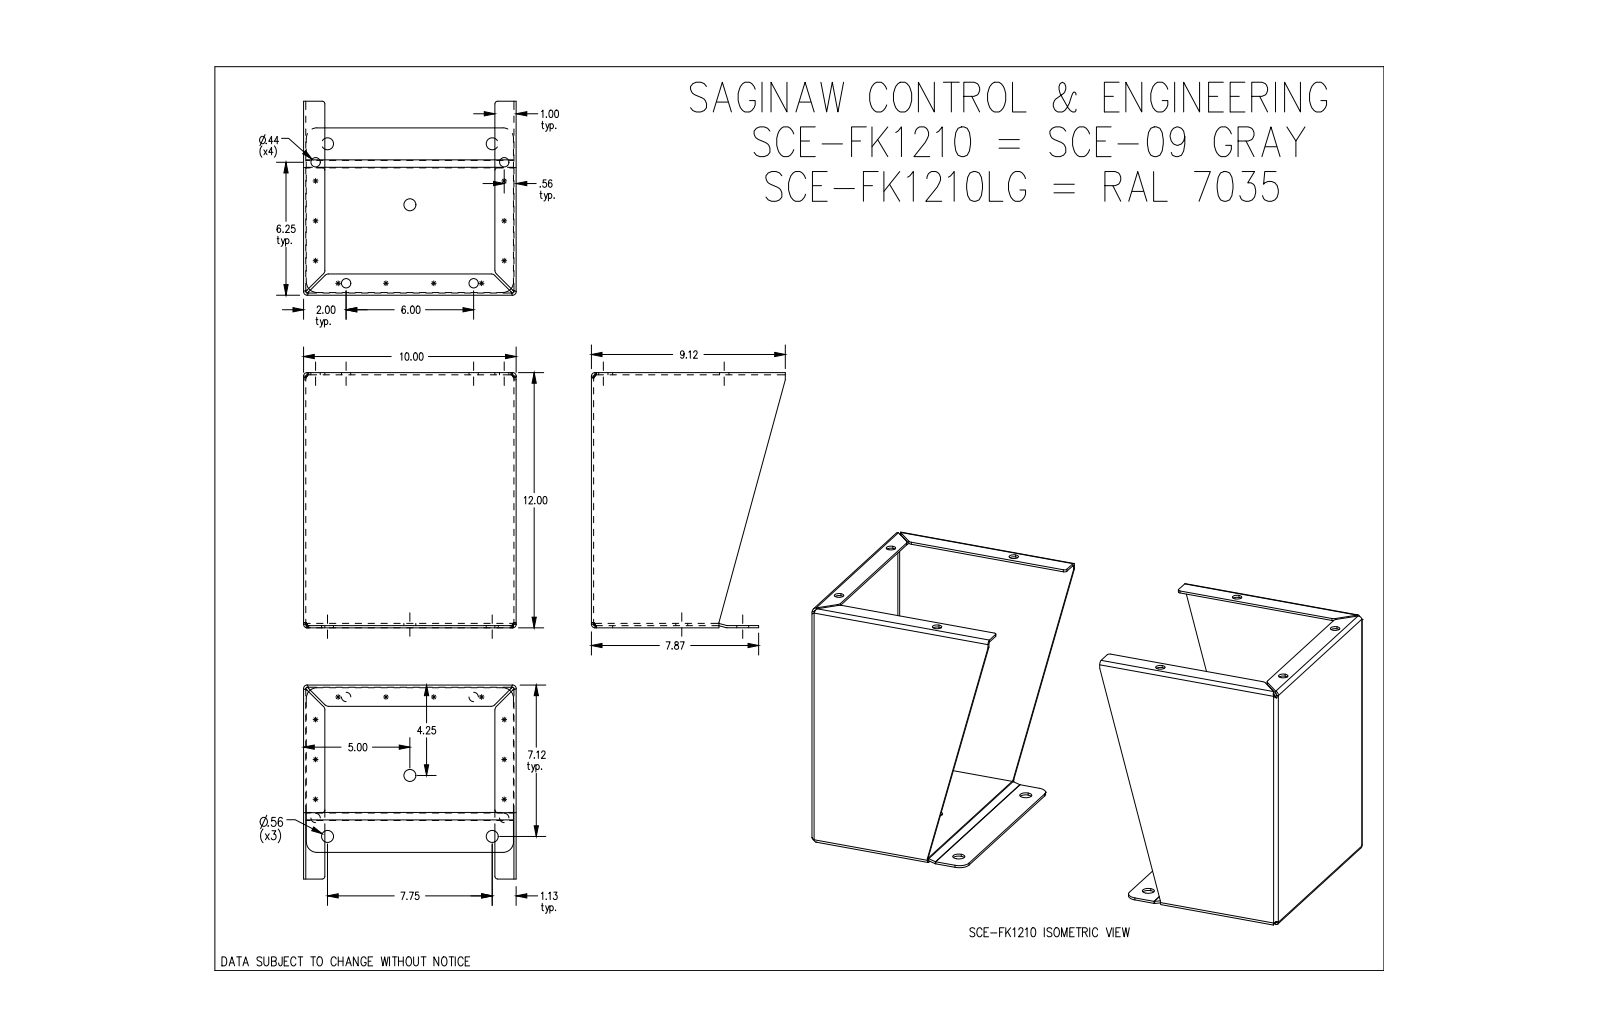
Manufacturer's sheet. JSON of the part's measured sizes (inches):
{"part_name": "SCE-FK1210", "step_written_by": "SolidWorks 2019 (CONFIG_CONTROL_DESIGN)", "units": "inches", "bodies": {"solids": 4, "faces": 214, "planar": 96, "cylindrical": 86, "other": 32}, "overall_size": [24, 12, 10], "volume_in3": 85.29, "surface_area_in2": 1667, "round_holes": [[0.437, 8], [0.563, 6]], "partial_cylinders_radius": [[0.166, 16], [0.063, 12], [0.125, 8], [0.22, 8], [0.5, 8], [0.062, 6]], "face_to_face_distances": [0.104, 9.896, 23.896, 9.792, 10, 23.792, 24, 11.792, 11.896, 0.101], "hole_center_spacings": [1.035, 4.755, 4.867, 5.866, 6.614, 9.363, 10.646, 13.211]}
